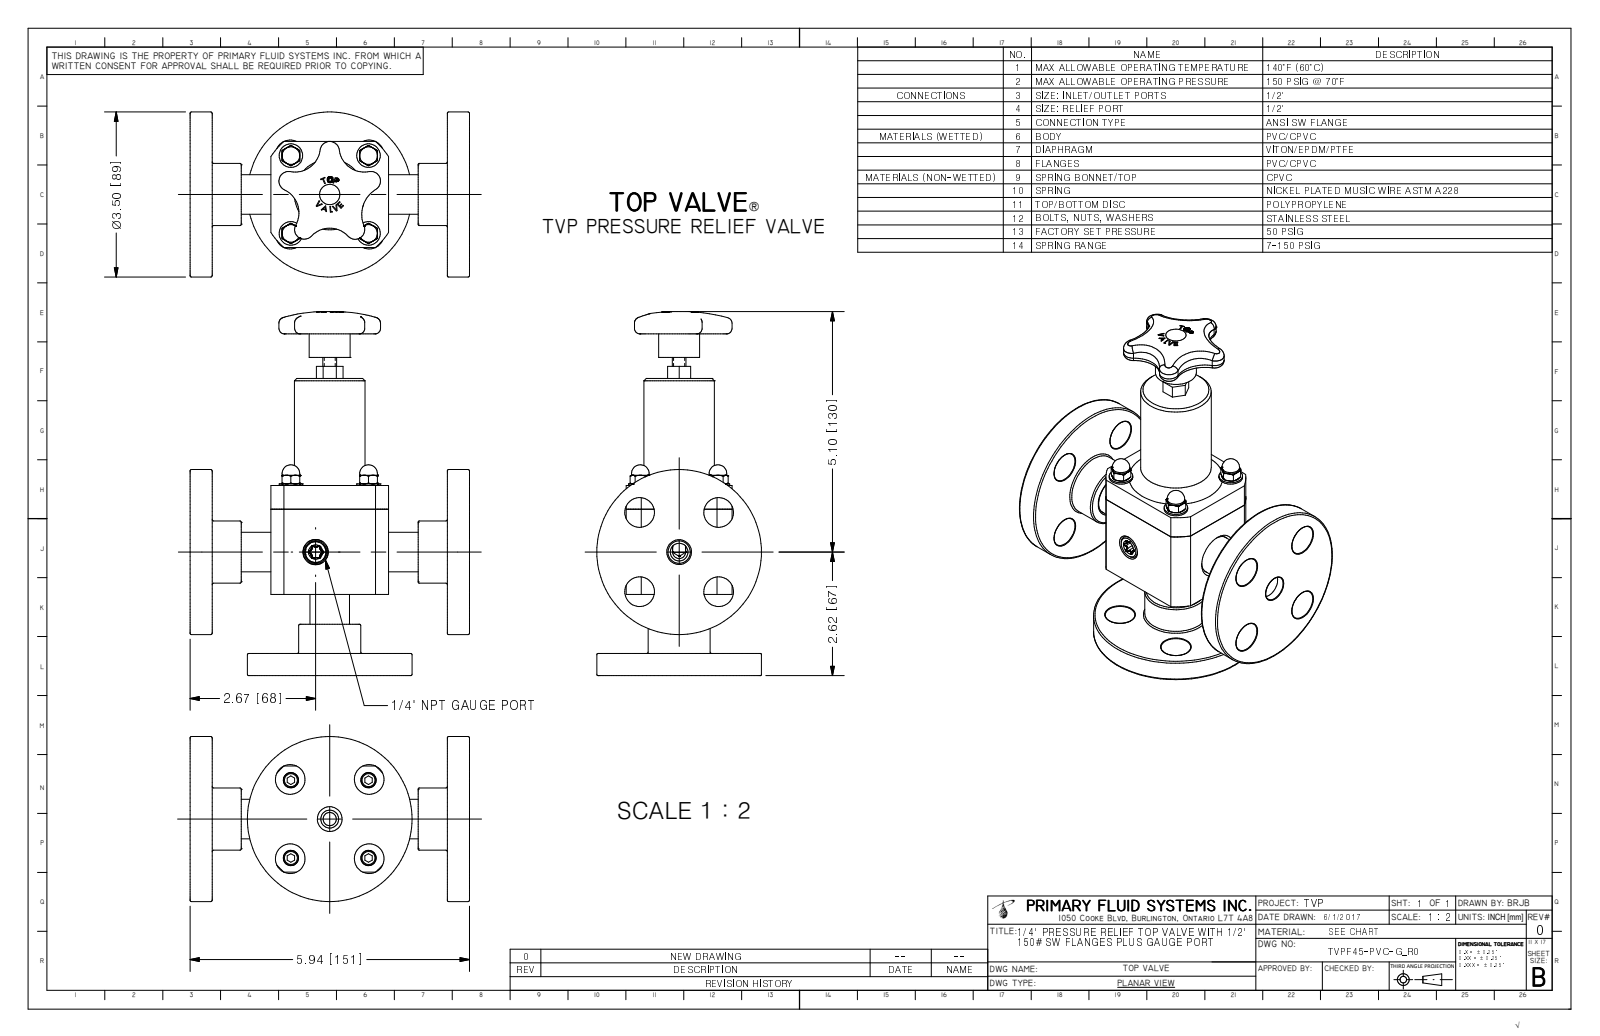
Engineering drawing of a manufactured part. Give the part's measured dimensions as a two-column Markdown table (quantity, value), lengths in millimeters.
| quantity | value |
| --- | --- |
| part name | TVPF45-PVC-G_R0 |
| STEP written by | Autodesk Inventor 2009 (AUTOMOTIVE_DESIGN) |
| units | millimeters |
| bodies | 1 solid, 462 faces (168 planar, 72 cylindrical, 222 other) |
| overall size | 196.1 × 150.9 × 88.9 |
| volume | 522 600 mm³ |
| surface area | 107 400 mm² |
| round holes (diameter × count) | 16 × 8, 3.7 × 4, 13.4 × 2, 38.7 × 1 |
| round bosses / shafts (diameter × count) | 12.7 × 4, 9.5 × 4, 7.9 × 4, 88.9 × 2, 33.5 × 2, 38.1 × 1, 22.1 × 1, 7.4 × 1 |
| partial cylindrical surfaces (radius × count) | 0.7 × 6, 2.2 × 5, 5.2 × 5, 13.6 × 4, 16.7 × 4, 15.9 × 1, 18.9 × 1, 37.8 × 1 |
| main face-to-face distances | 11.9, 138.9, 43.7, 31.8, 150.9, 127, 107.2, 95.3, 57.2, 63.5 |
| hole center spacings | 30.2, 42.7, 42.3, 60.3, 0.5, 0.5, 29.6, 29.6 |
